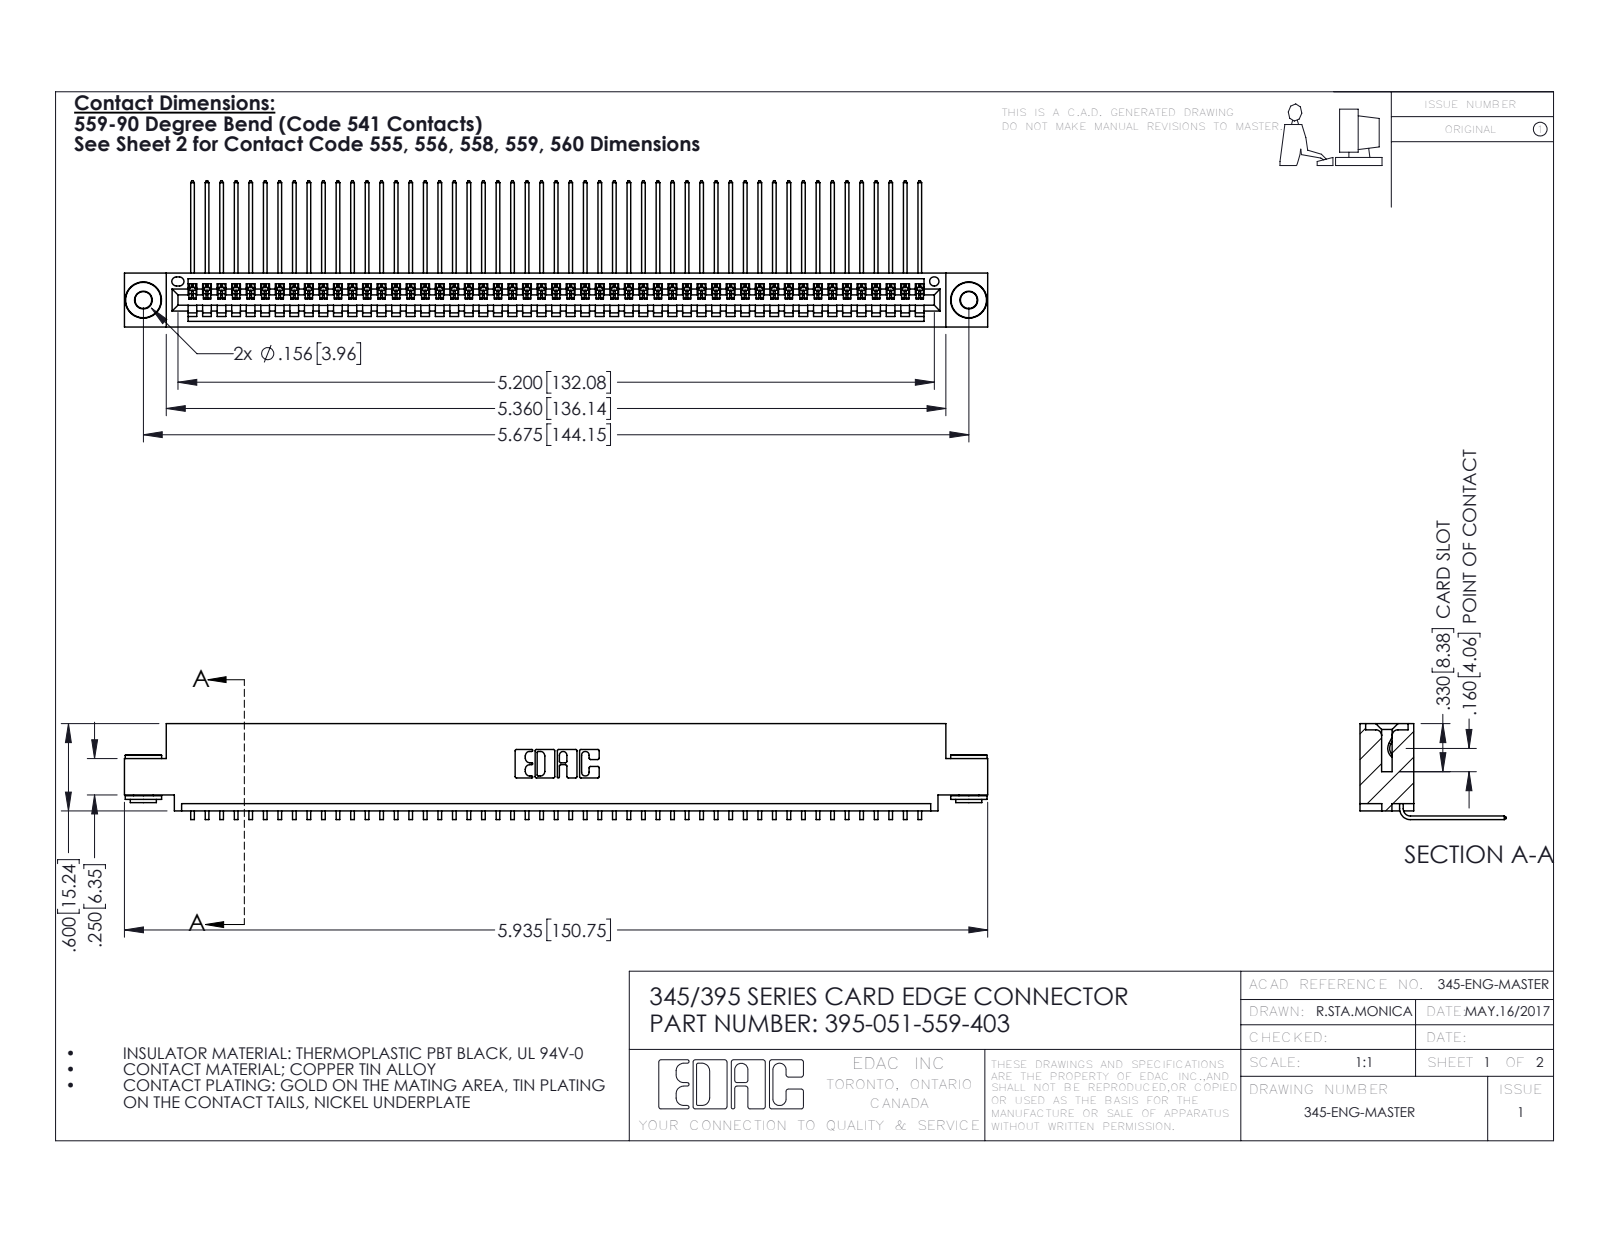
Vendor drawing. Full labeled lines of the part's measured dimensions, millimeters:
Part name (STEP PRODUCT): 345-292-001_558 559 Tail - 1; 395-051-559-403; 345-250-002_345-250-002-102; 345 Part_0.110 Offset - 0.156 Dia-TH
STEP written by: SolidWorks 2016 (CONFIG_CONTROL_DESIGN)
Units: millimetres
Bodies: 54 solids, 3228 faces (2236 planar, 984 cylindrical, 8 other)
Overall size (bounding box): 150.7 × 25.5 × 16.7
Volume: 14 500 mm³ · Surface area: 20 700 mm²
Round holes (diameter × count): ⌀2.9 ×2, ⌀4 ×2, ⌀1.6 ×1
Round bosses / shafts (diameter × count): ⌀6.4 ×2, ⌀4.6 ×2, ⌀3.5 ×2
Partial cylindrical surfaces — rounded edges, fillets, slot ends (radius × count): R0.2 ×102, R0.3 ×22, R0.2 ×6, R0.8 ×6, R0.7 ×3, R0.8 ×2, R1 ×2, R0.4 ×1
Main face-to-face distances: 1.8, 7.6, 9.4, 5.1, 0.6, 2.5, 6.9, 5.7, 3.8, 1.8
Hole centre spacings: 6.9, 138.2, 144.1
